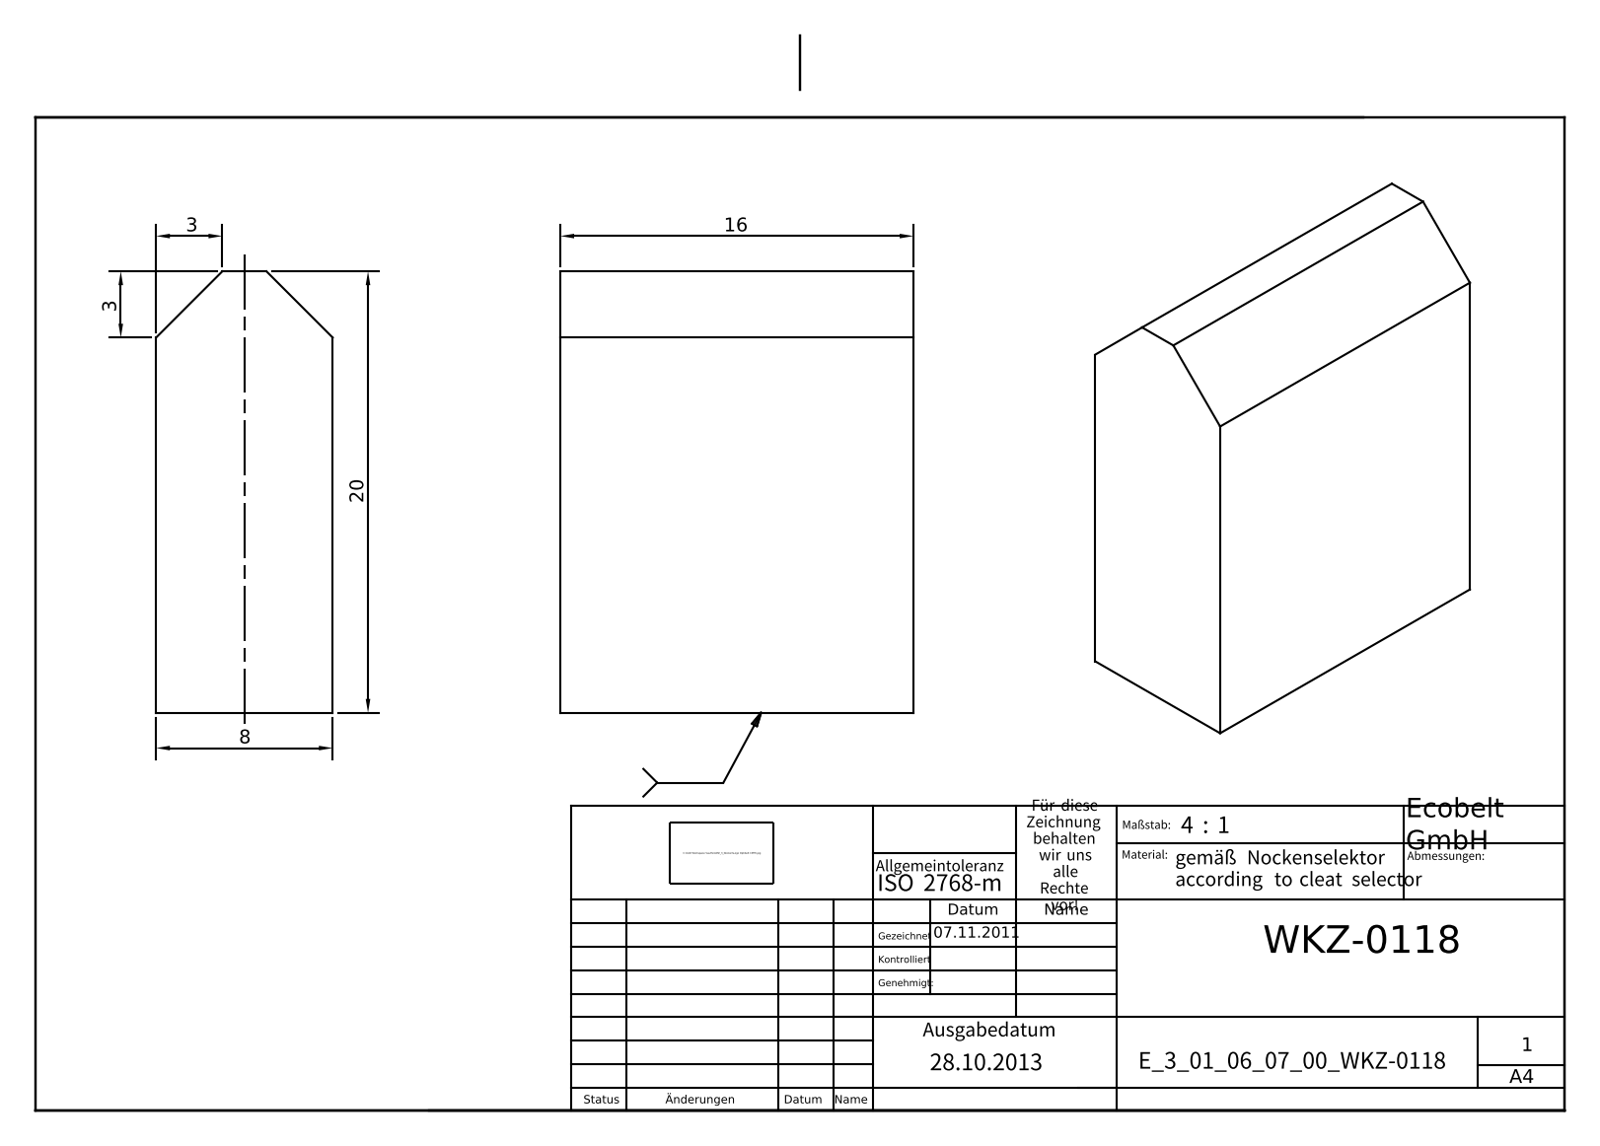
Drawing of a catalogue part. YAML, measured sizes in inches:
part_name: "E_3_01_06_07_00_WKZ-0118"
step_written_by: "Autodesk Inventor 2025 (AUTOMOTIVE_DESIGN)"
units: inches
bodies: {solids: 1, faces: 8, planar: 8, cylindrical: 0, other: 0}
overall_size: [0.787, 0.63, 0.315]
volume: 0.147
surface_area: 1.77
face_to_face_distances: [0.315, 0.63, 0.787]
